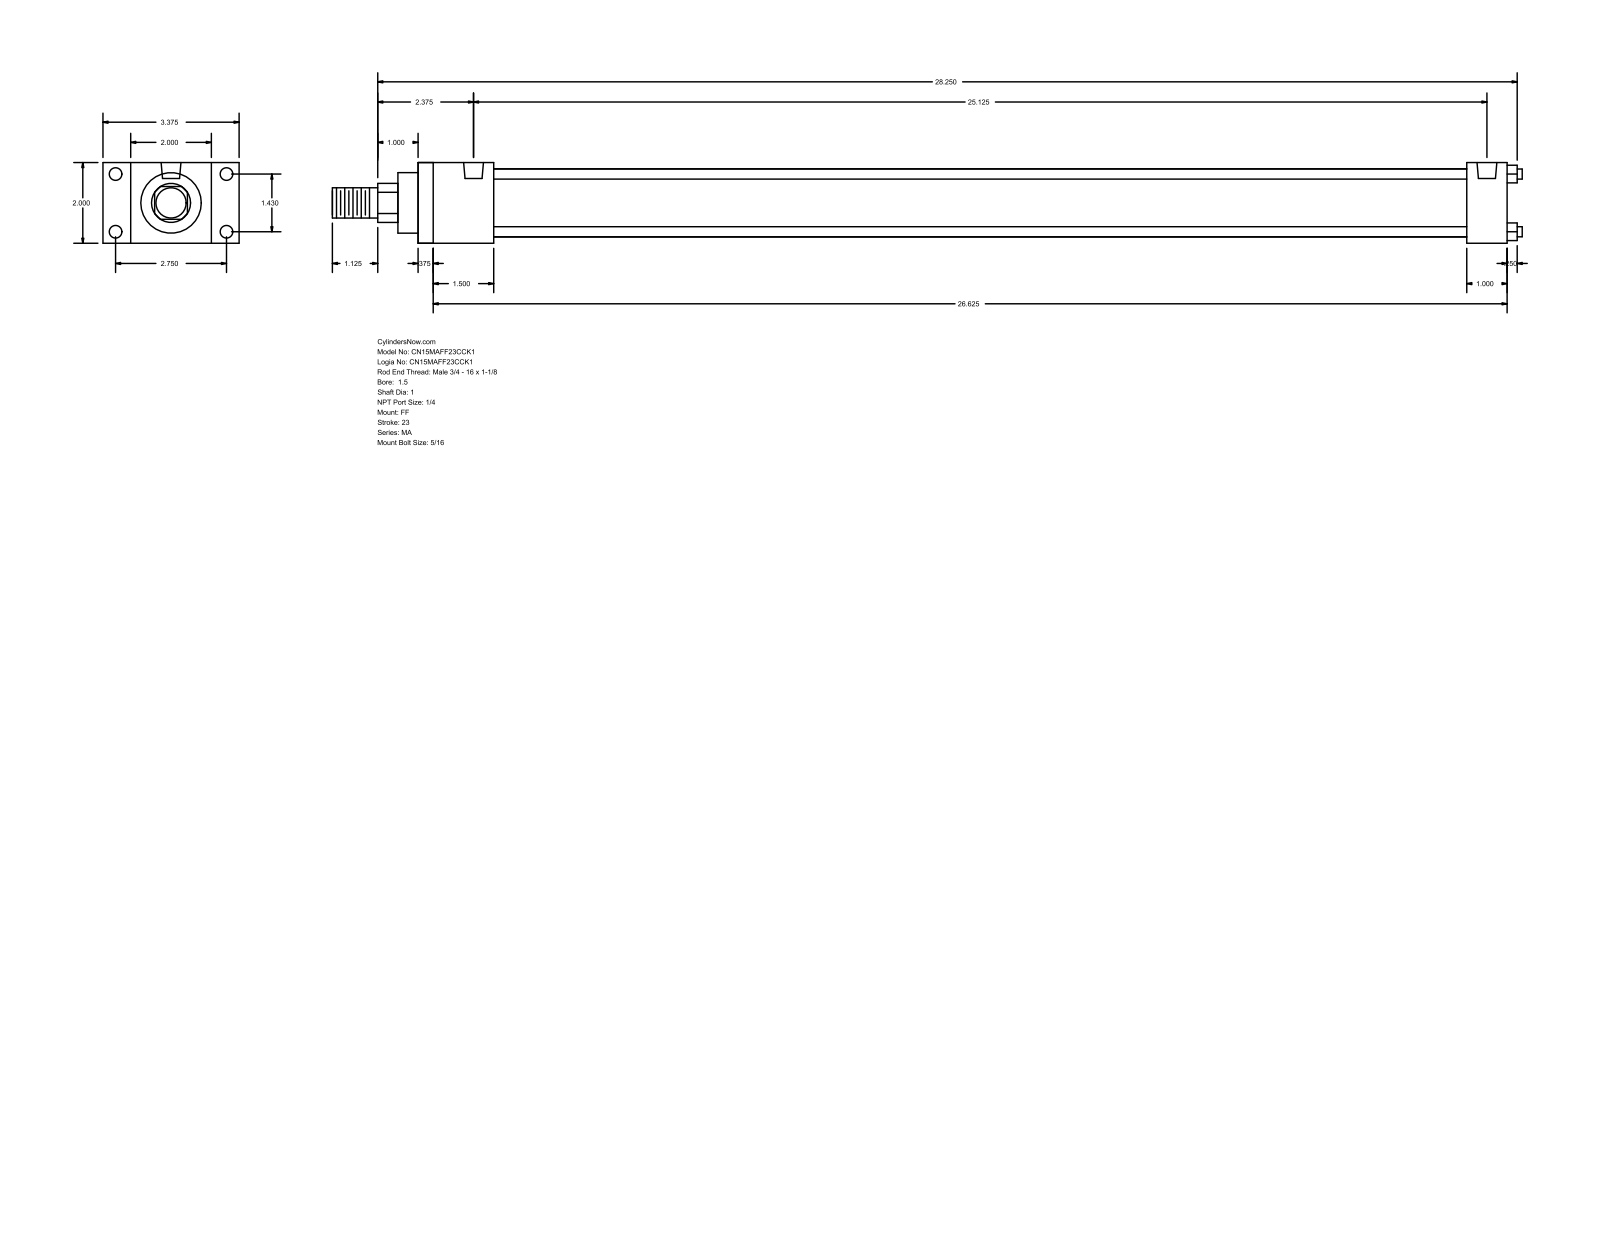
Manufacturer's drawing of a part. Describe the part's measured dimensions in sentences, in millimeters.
The part is named "MA_FF__0150_1". Its 3-D file was written by "GSSL Pune (CONFIG_CONTROL_DESIGN)". It is 0 solids with 92 faces: 64 planar, 28 cylindrical and 0 other. Overall it measures 749.3 by 85.72 by 50.8 millimeters. Round holes: 8 of diameter 7.94, 2 of diameter 12.49. Round bosses or shafts: 4 of diameter 6.35, 1 of diameter 42.93, 1 of diameter 38.1, 1 of diameter 25.4, 1 of diameter 19.05. Partial cylindrical surfaces (rounded edges, fillets, slot ends): 1 of radius 12.29. The main face-to-face distances are 50.8, 685.8, 9.52, 676.28, 25.4, 47.63, 660.4, 38.11, 650.88, 612.77. The hole center spacings are 36.32, 69.84, 78.72, 638.17.
